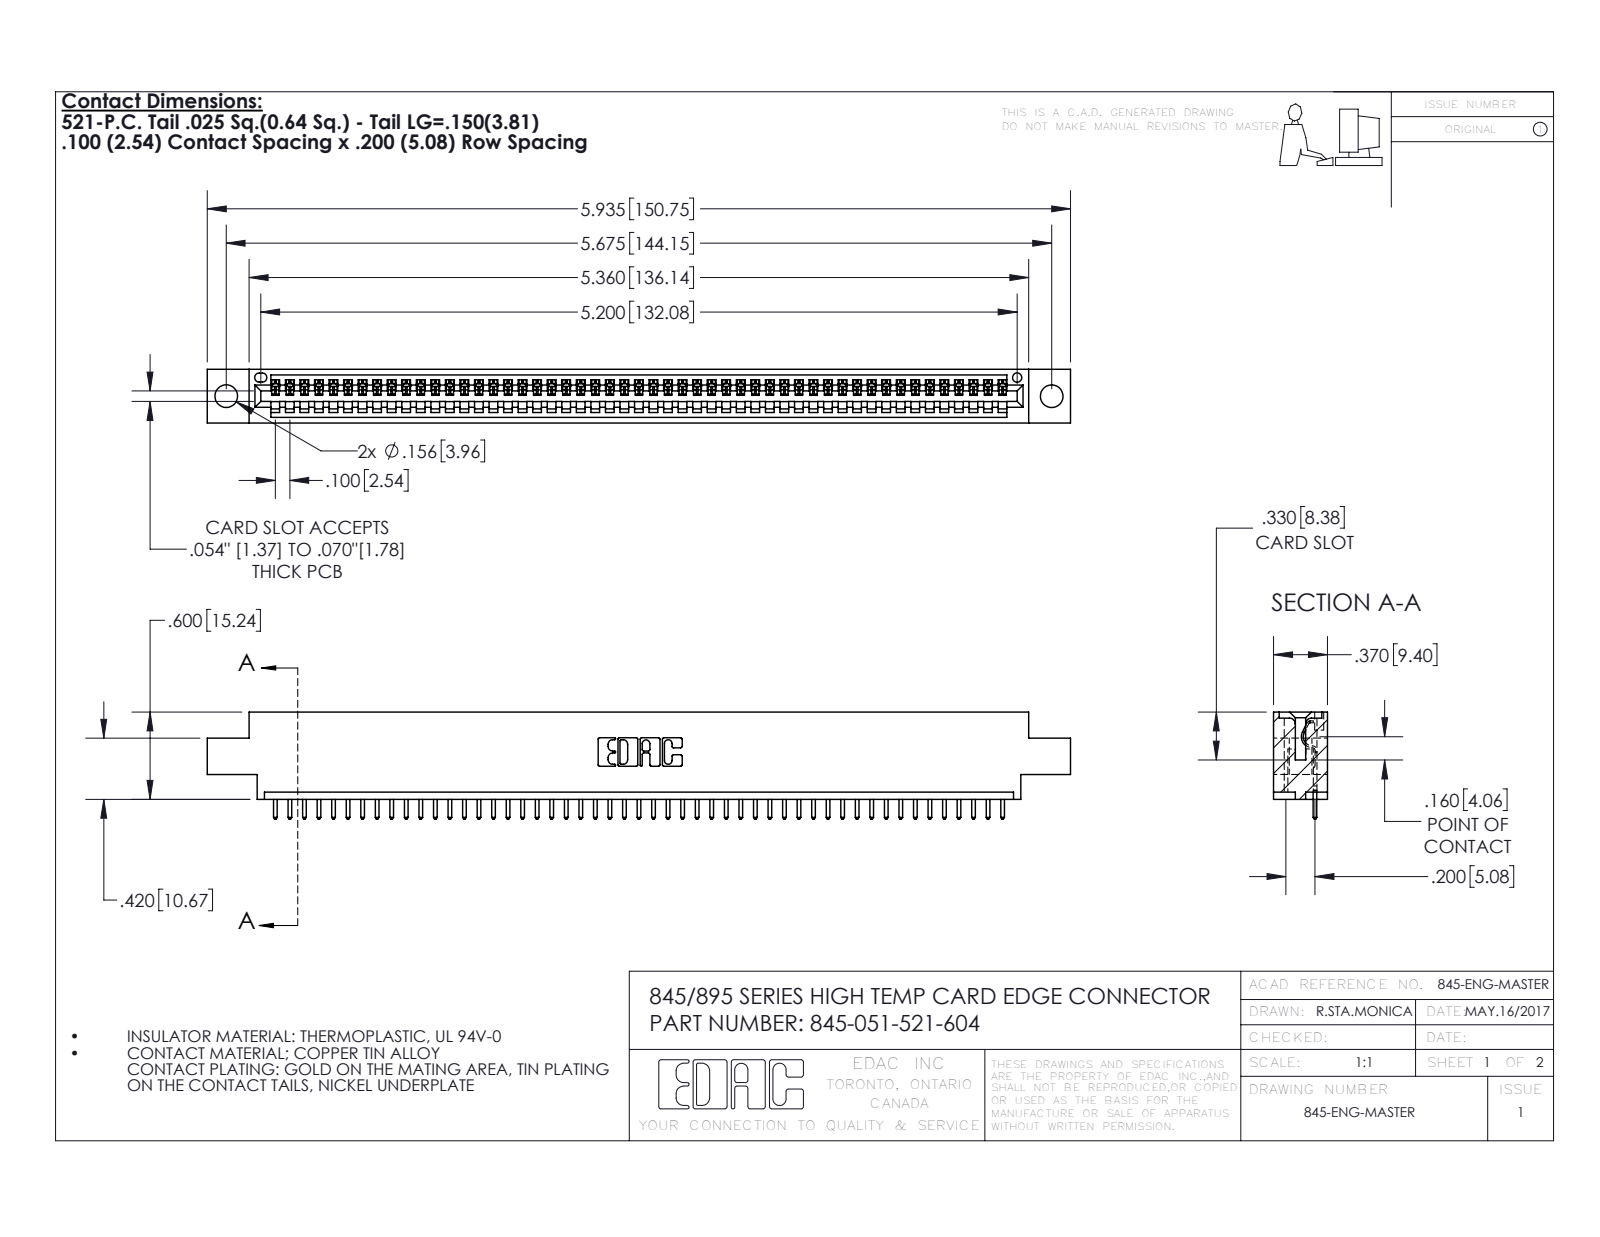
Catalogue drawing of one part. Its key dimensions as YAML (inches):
part_name: "345 Part_0.170 Offset - 0.156 Dia-TH; 345-292-001_345-293-121; 345-051-521-604"
step_written_by: "SolidWorks 2016 (CONFIG_CONTROL_DESIGN)"
units: inches
bodies: {solids: 52, faces: 3088, planar: 2124, cylindrical: 964, other: 0}
overall_size: [5.935, 0.737, 0.37]
volume: 0.857
surface_area: 28.14
round_holes:
  - {diameter: 0.156, count: 2}
  - {diameter: 0.064, count: 1}
partial_cylinders:
  - {radius: 0.006, count: 102}
  - {radius: 0.01, count: 102}
  - {radius: 0.01, count: 22}
  - {radius: 0.007, count: 6}
  - {radius: 0.031, count: 6}
  - {radius: 0.026, count: 3}
  - {radius: 0.031, count: 2}
  - {radius: 0.04, count: 2}
face_to_face_distances: [0.298, 0.072, 0.37, 0.2, 0.098, 0.272, 0.025, 0.225, 0.175, 0.149]
hole_center_spacings: [0.27, 5.439, 5.675]
